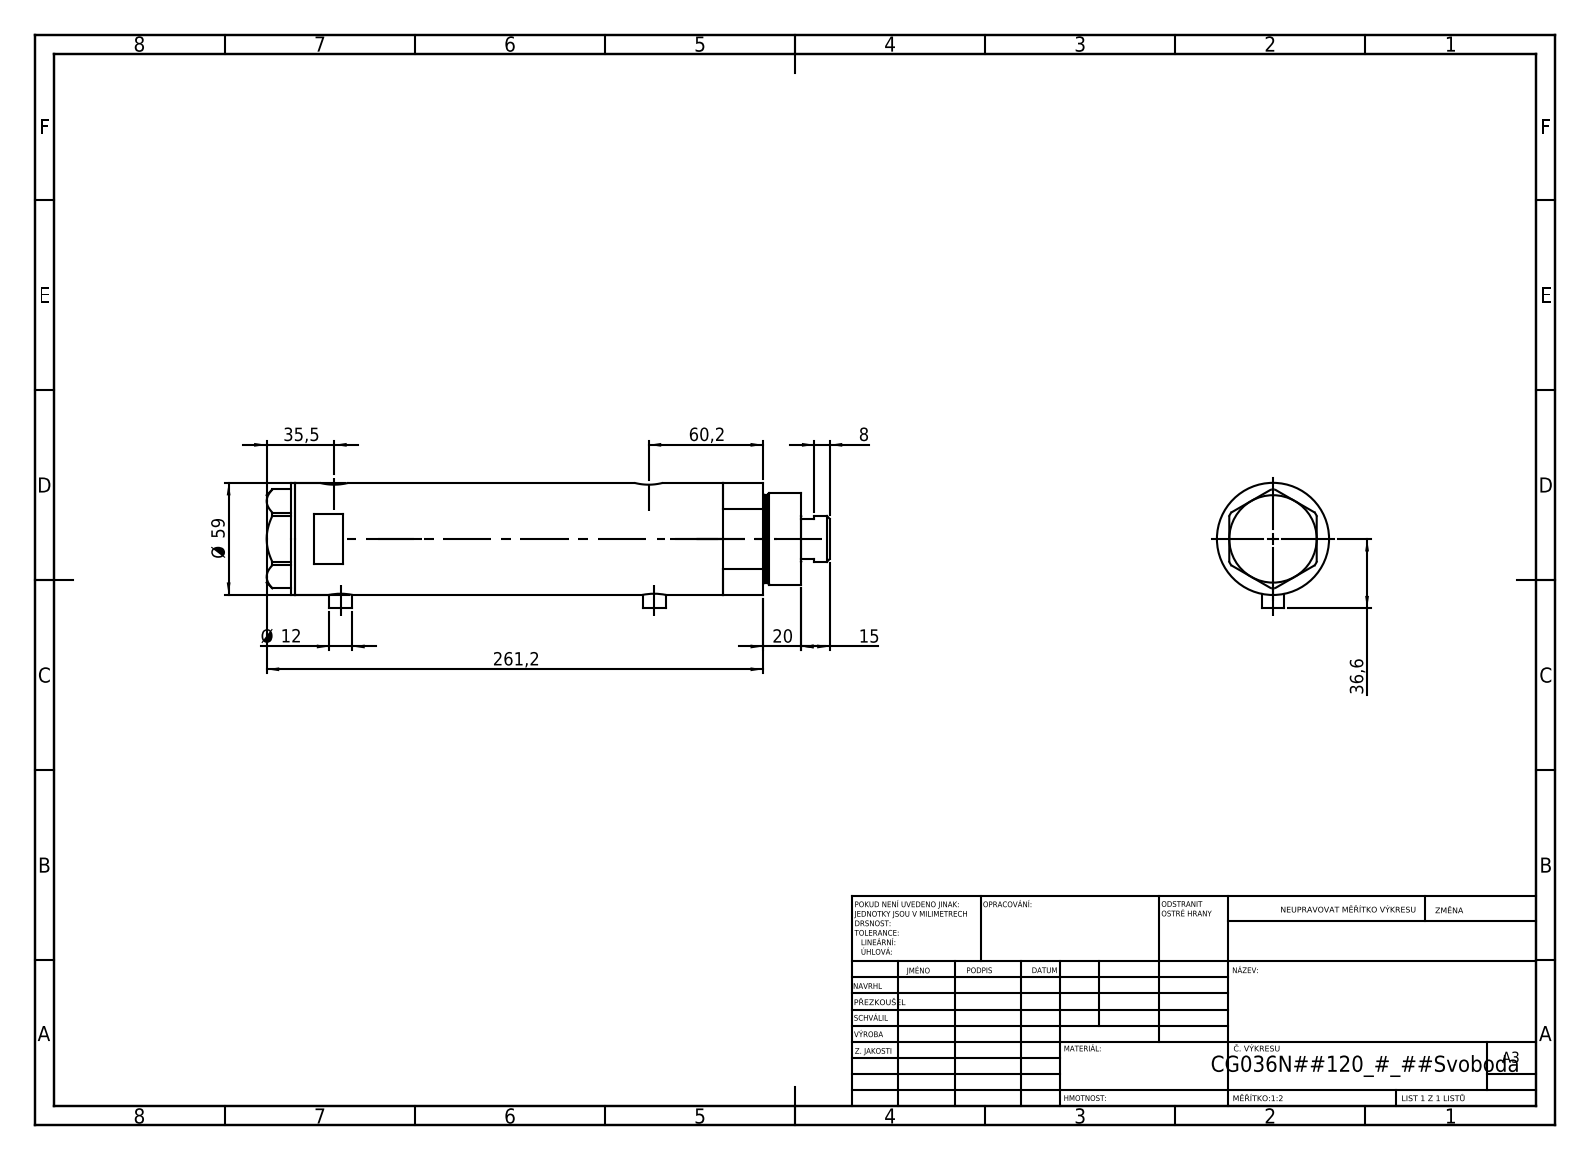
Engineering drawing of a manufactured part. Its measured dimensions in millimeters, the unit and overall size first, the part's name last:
Units: millimetres
Overall size (bounding box): 296.25 × 66.1 × 59
Round holes (diameter × count): ⌀5 ×2, ⌀9.73 ×2, ⌀12.5 ×2, ⌀15 ×2, ⌀8.5 ×1, ⌀25 ×1, ⌀26.5 ×1, ⌀36 ×1, ⌀40 ×1, ⌀52 ×1
Round bosses / shafts (diameter × count): ⌀12 ×2, ⌀59 ×1, ⌀48 ×1, ⌀46 ×1, ⌀24 ×1
Main face-to-face distances: 187.2, 23.5, 163.7, 15, 38.5, 202.2, 2, 266.2, 281.2, 242.7
Hole centre spacings: 2.9, 3.5, 162, 164.9, 165.5, 168.4
Volume: 673 416 mm³ · Surface area: 132 906 mm²
Bodies: 4 solids, 126 faces (53 planar, 53 cylindrical, 20 other)
Part name (STEP PRODUCT): V270CG_MIDDLE; V270CG_BACK; V270CG_FRONT; V270CG_VC
STEP written by: SolidWorks 2019 (CONFIG_CONTROL_DESIGN)
